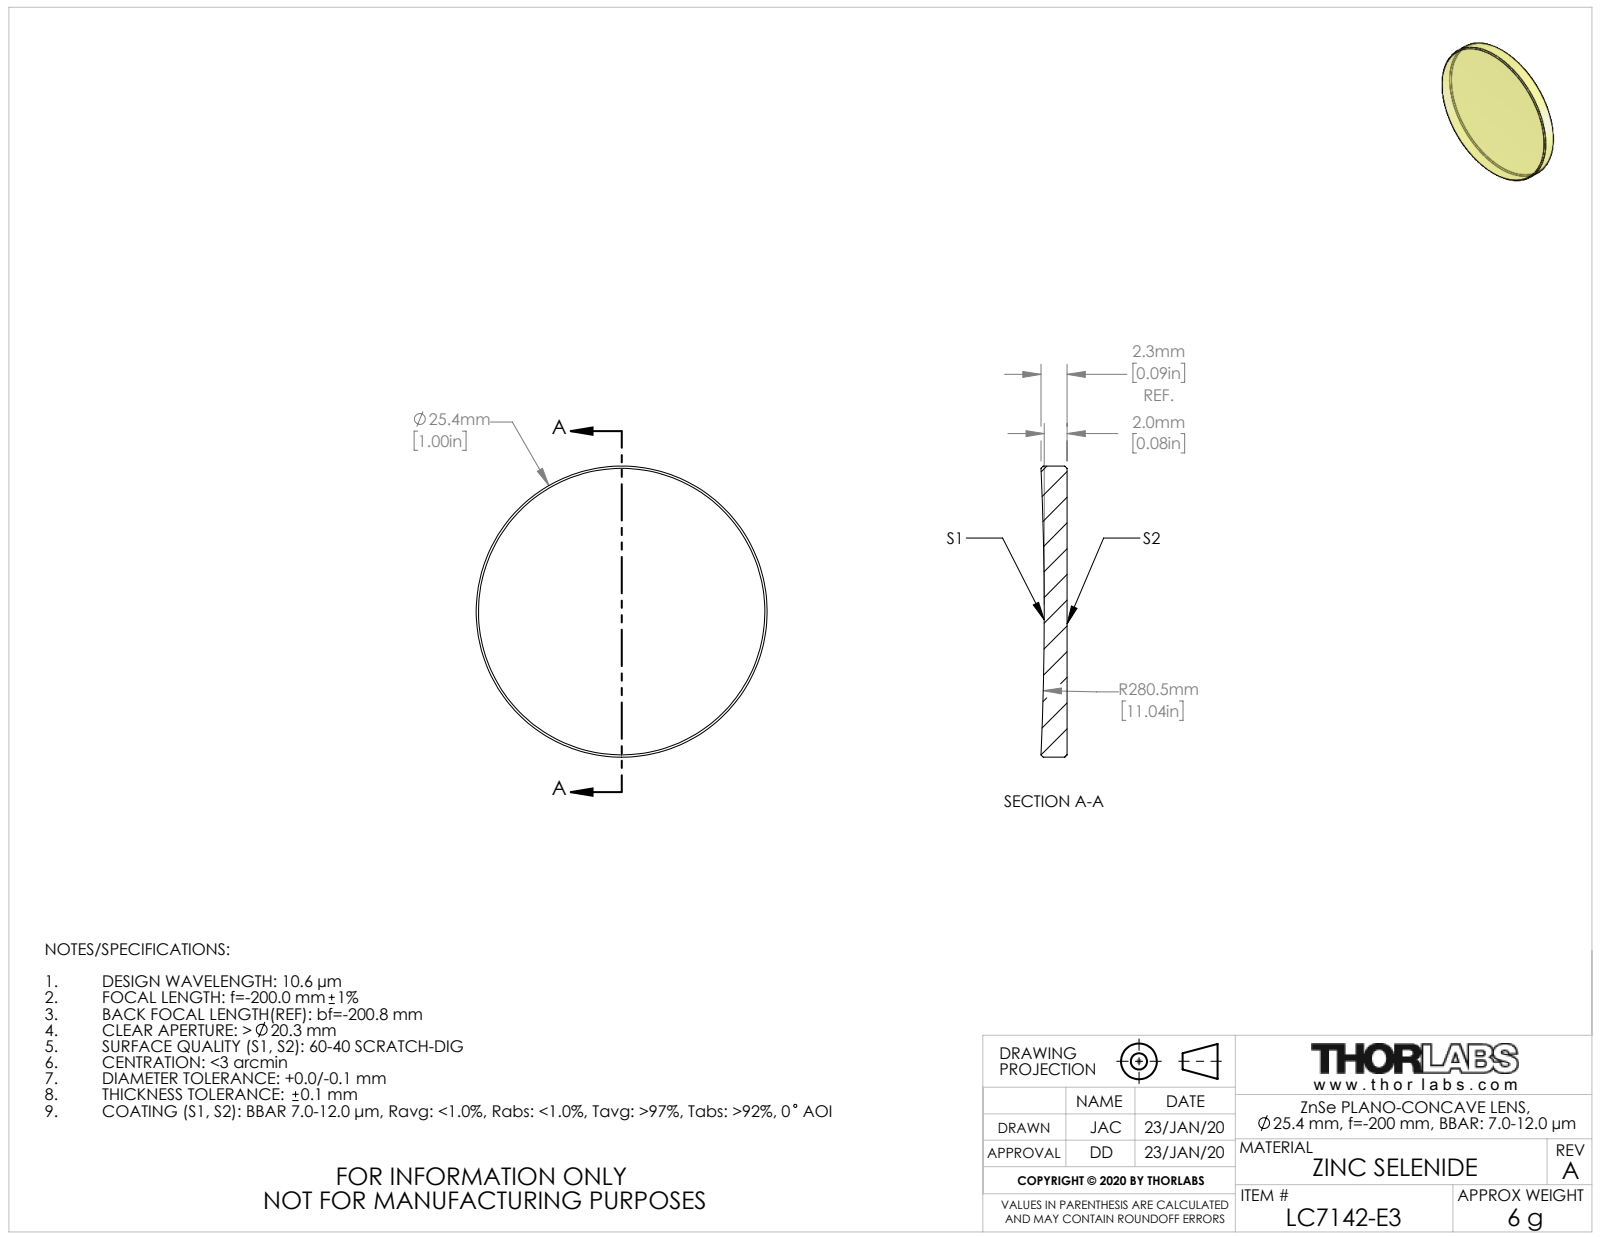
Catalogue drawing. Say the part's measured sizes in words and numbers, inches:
The part is named "TTN206862-E0W". Its 3-D file was written by "SolidWorks 2018 (CONFIG_CONTROL_DESIGN)". It is 1 solid with 9 faces: 1 planar, 2 cylindrical and 6 other. Overall it measures 1 by 1 by 0.09 inches. Its volume is 0.066 cubic inches and its surface area 1.824 square inches. Round bosses or shafts: 1 of diameter 1.
